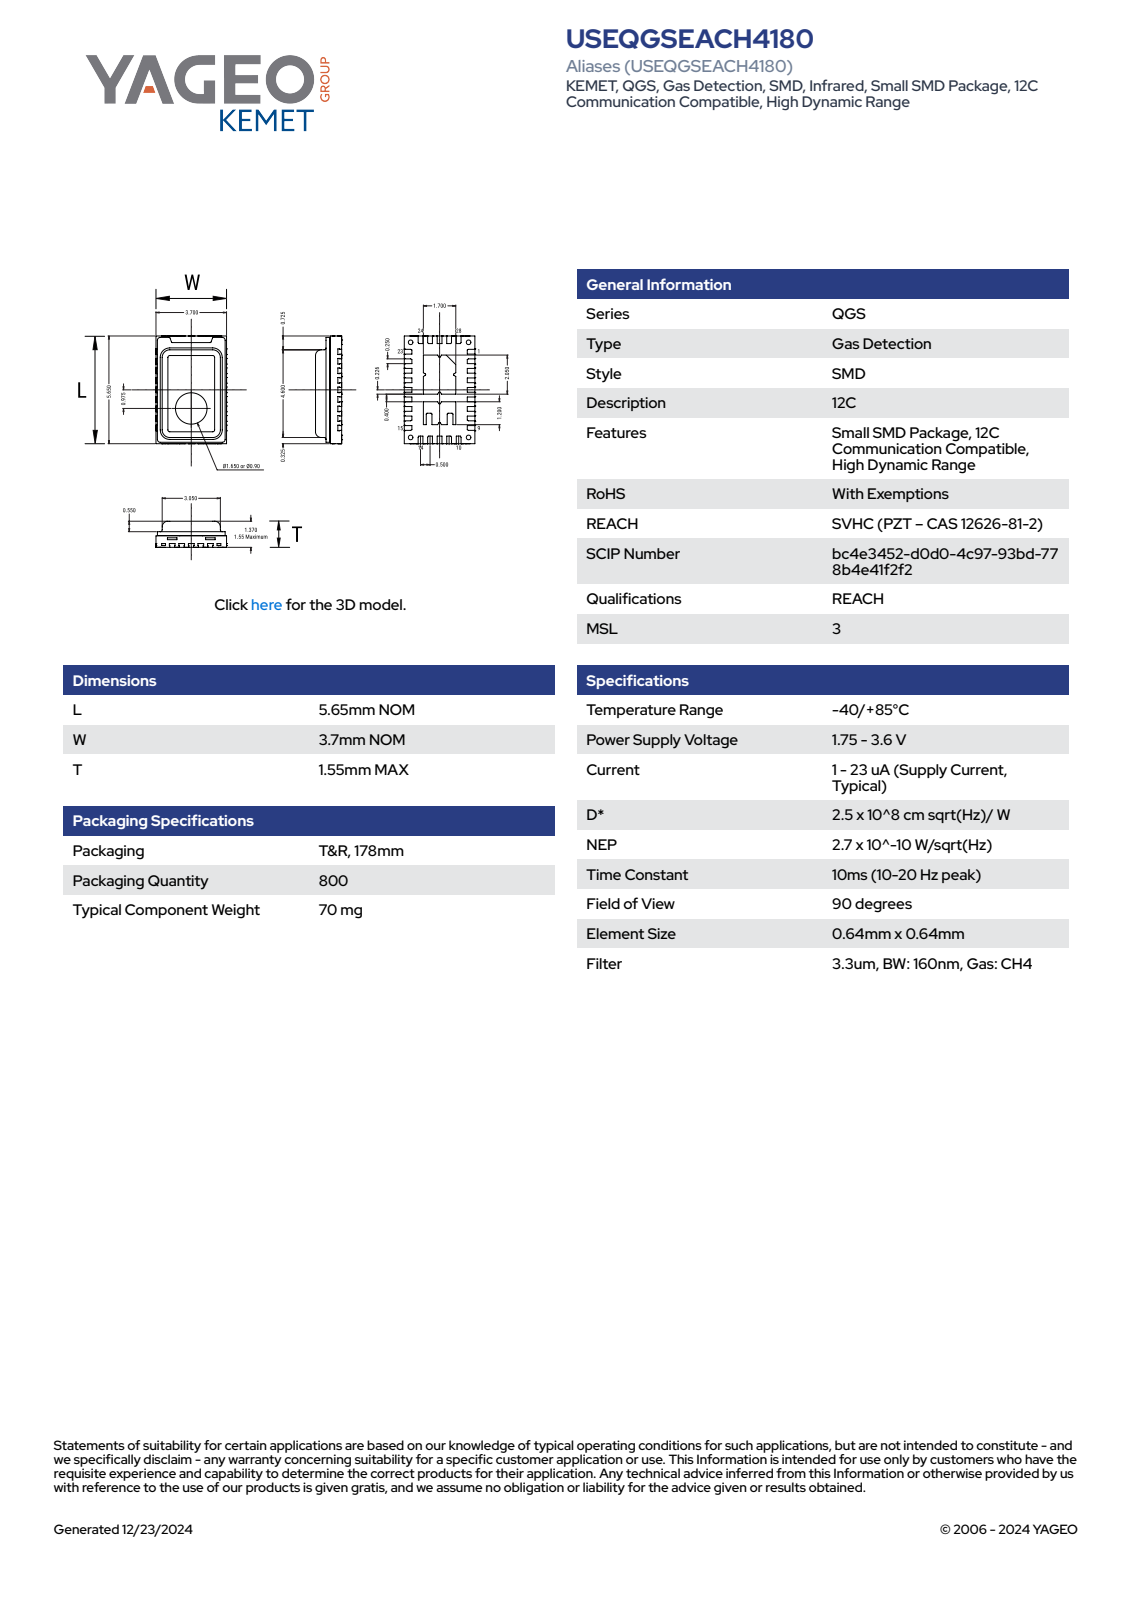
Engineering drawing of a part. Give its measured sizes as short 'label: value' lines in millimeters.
name: SF_QGS_L5.65W3.7T1.55
written by: SolidWorks 2014 (AUTOMOTIVE_DESIGN)
unit: mm
bodies: 1 solid, 97 faces (71 planar, 18 cylindrical, 8 other)
size: 5.65 × 3.7 × 1.55
volume: 28 mm³; area: 67 mm²
holes: 1× ⌀1.65
rounds: 8× R0.1, 8× R0.15
face distances: 1.55, 3.7, 0.55, 1, 5.65, 0.5, 1.5, 0.33, 0.85, 0.65
